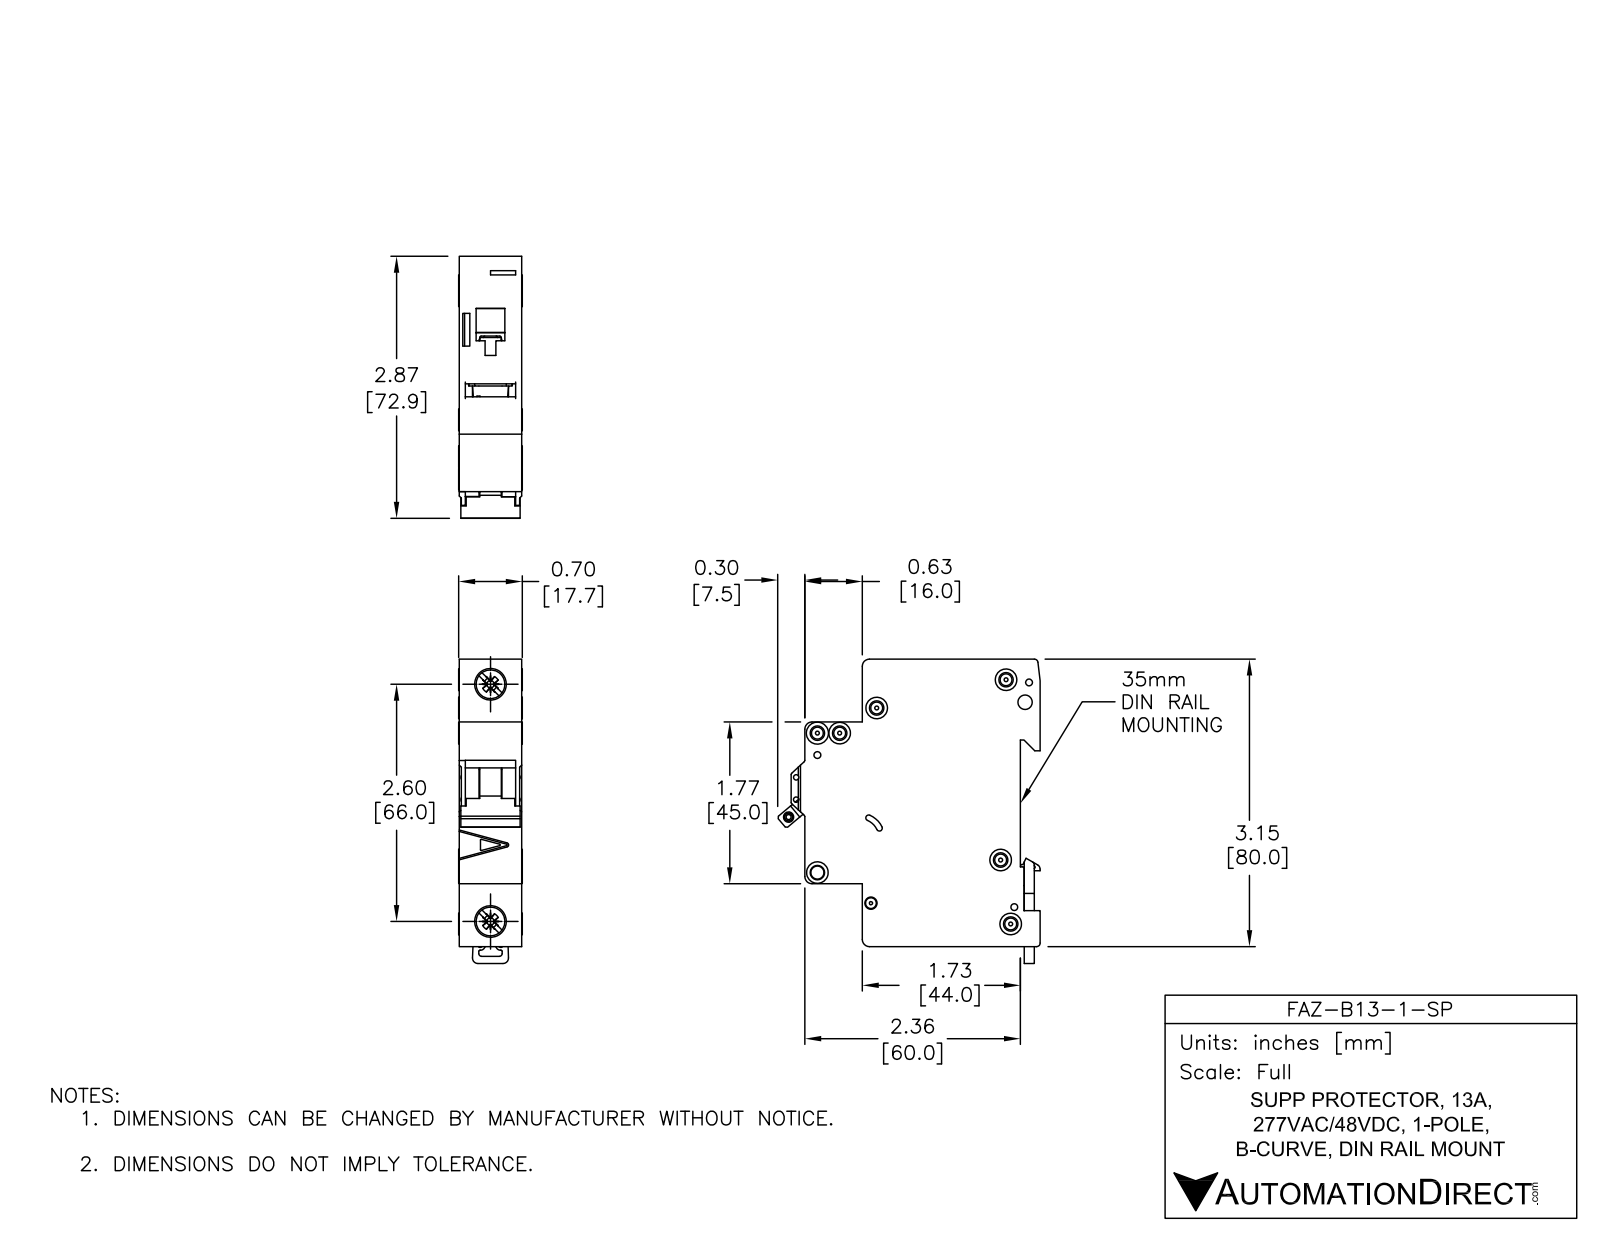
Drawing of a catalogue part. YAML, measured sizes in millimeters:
part_name: "FAZ-B13-1-SP"
step_written_by: "SolidWorks 2014 (AUTOMOTIVE_DESIGN)"
units: millimeters
bodies: {solids: 5, faces: 558, planar: 235, cylindrical: 202, other: 121}
overall_size: [84.78, 73.04, 17.7]
volume: 74935
surface_area: 19545
round_holes:
  - {diameter: 3.6, count: 6}
  - {diameter: 1.9, count: 3}
  - {diameter: 1.09, count: 2}
  - {diameter: 1.5, count: 2}
  - {diameter: 4, count: 2}
  - {diameter: 7.15, count: 2}
  - {diameter: 2.15, count: 1}
  - {diameter: 2.2, count: 1}
  - {diameter: 2.55, count: 1}
  - {diameter: 3.3, count: 1}
  - {diameter: 3.4, count: 1}
round_bosses_or_shafts:
  - {diameter: 6, count: 4}
  - {diameter: 8.2, count: 2}
  - {diameter: 2.5, count: 1}
partial_cylinders:
  - {radius: 0.25, count: 30}
  - {radius: 0.5, count: 13}
  - {radius: 2, count: 8}
  - {radius: 0.2, count: 5}
  - {radius: 1, count: 4}
  - {radius: 0.8, count: 2}
  - {radius: 3, count: 2}
  - {radius: 1.5, count: 1}
face_to_face_distances: [17.5, 79.48, 5.5, 49.5, 44, 65.5, 60, 16, 1.75, 15.75]
hole_center_spacings: [6.2, 13.64, 4.81, 5.19, 5.61, 6.1, 6.44, 8.19]
